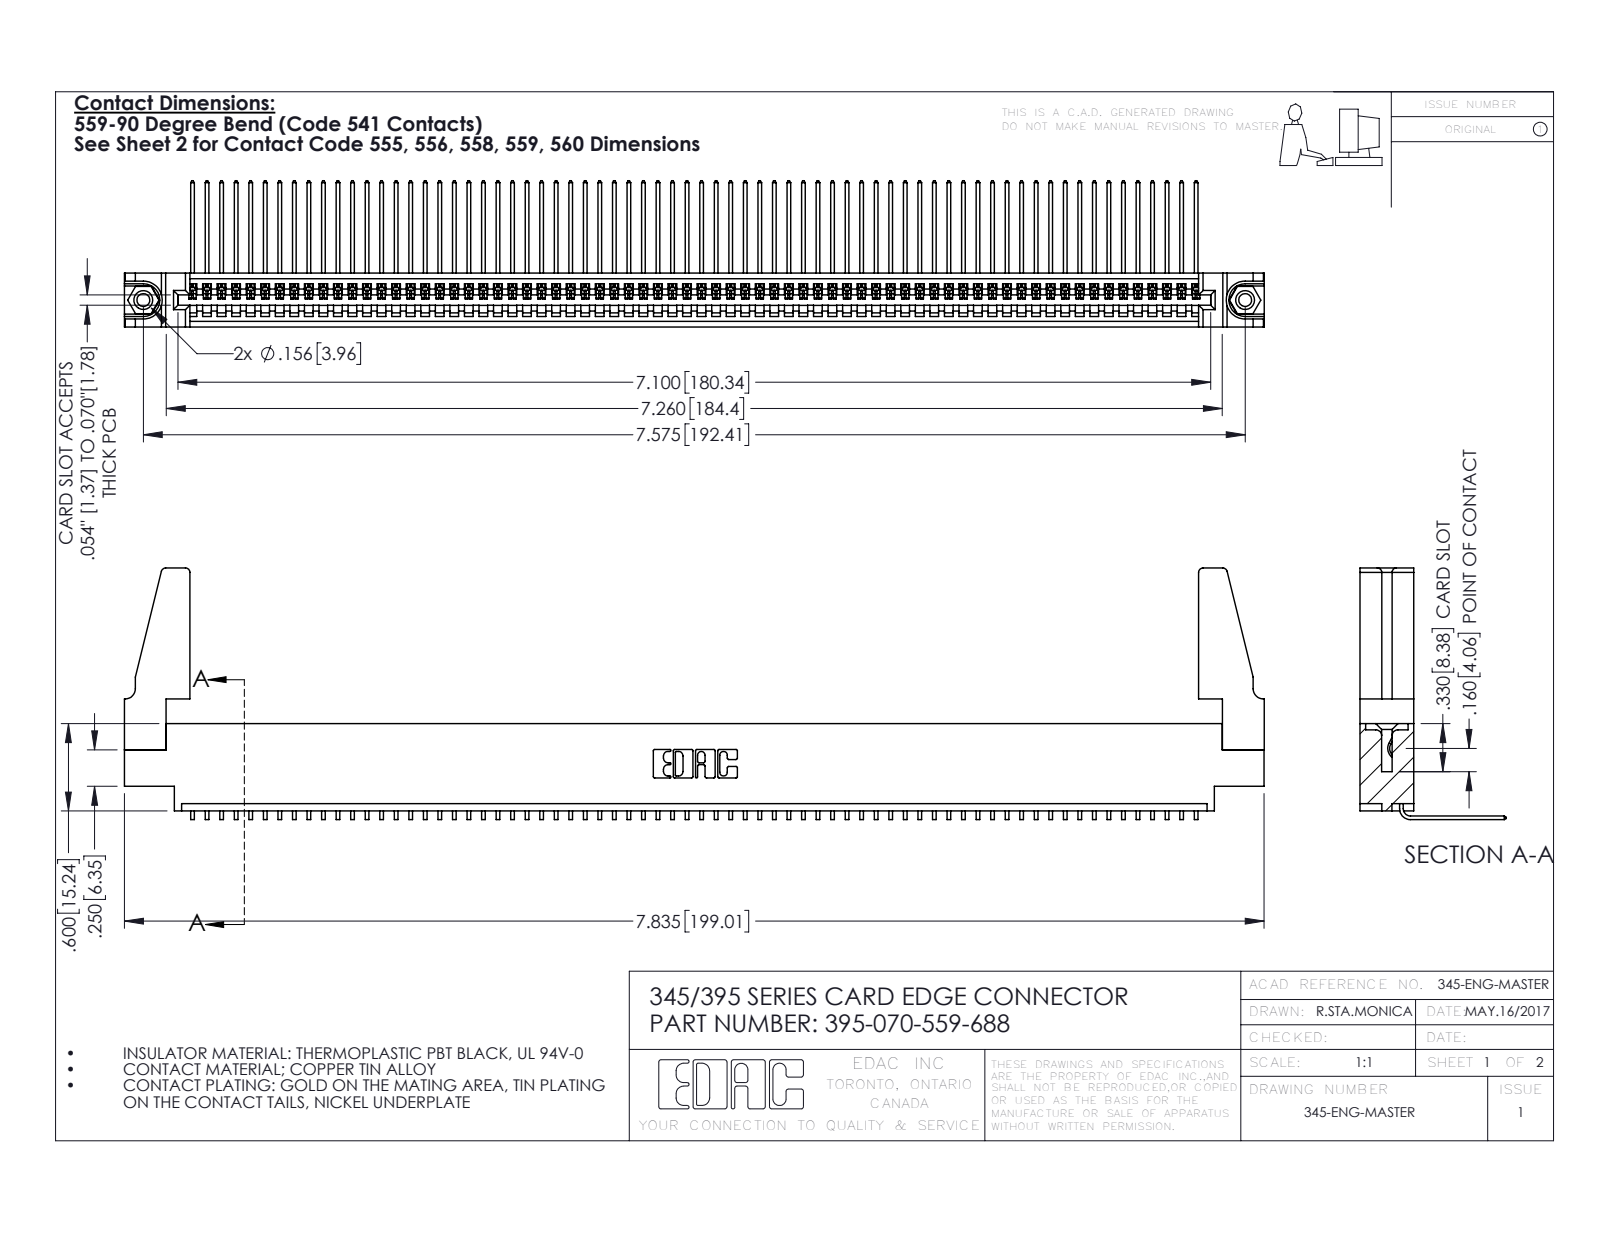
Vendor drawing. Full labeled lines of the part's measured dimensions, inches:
Part name (STEP PRODUCT): 345-220-078_345-220-088; 345-292-001_558 559 Tail - 1; 345 Part_0.170 Offset - 0.156 Dia-TH; 395-070-559-688 (+1 more)
STEP written by: SolidWorks 2016 (CONFIG_CONTROL_DESIGN)
Units: inches
Bodies: 75 solids, 4454 faces (3096 planar, 1342 cylindrical, 16 other)
Overall size (bounding box): 7.836 × 1.729 × 1.005
Volume: 1.373 in³ · Surface area: 47.42 in²
Round holes (diameter × count): ⌀0.089 ×2, ⌀0.125 ×2, ⌀0.156 ×2, ⌀0.064 ×1
Round bosses / shafts (diameter × count): ⌀0.155 ×2
Partial cylindrical surfaces — rounded edges, fillets, slot ends (radius × count): R0.006 ×140, R0.01 ×22, R0.03 ×8, R0.007 ×6, R0.031 ×6, R0.026 ×3, R0.031 ×2, R0.04 ×2
Main face-to-face distances: 0.072, 0.298, 0.37, 0.2, 0.098, 0.272, 0.025, 0.225, 0.175, 0.149
Hole centre spacings: 0.27, 7.339, 7.575
